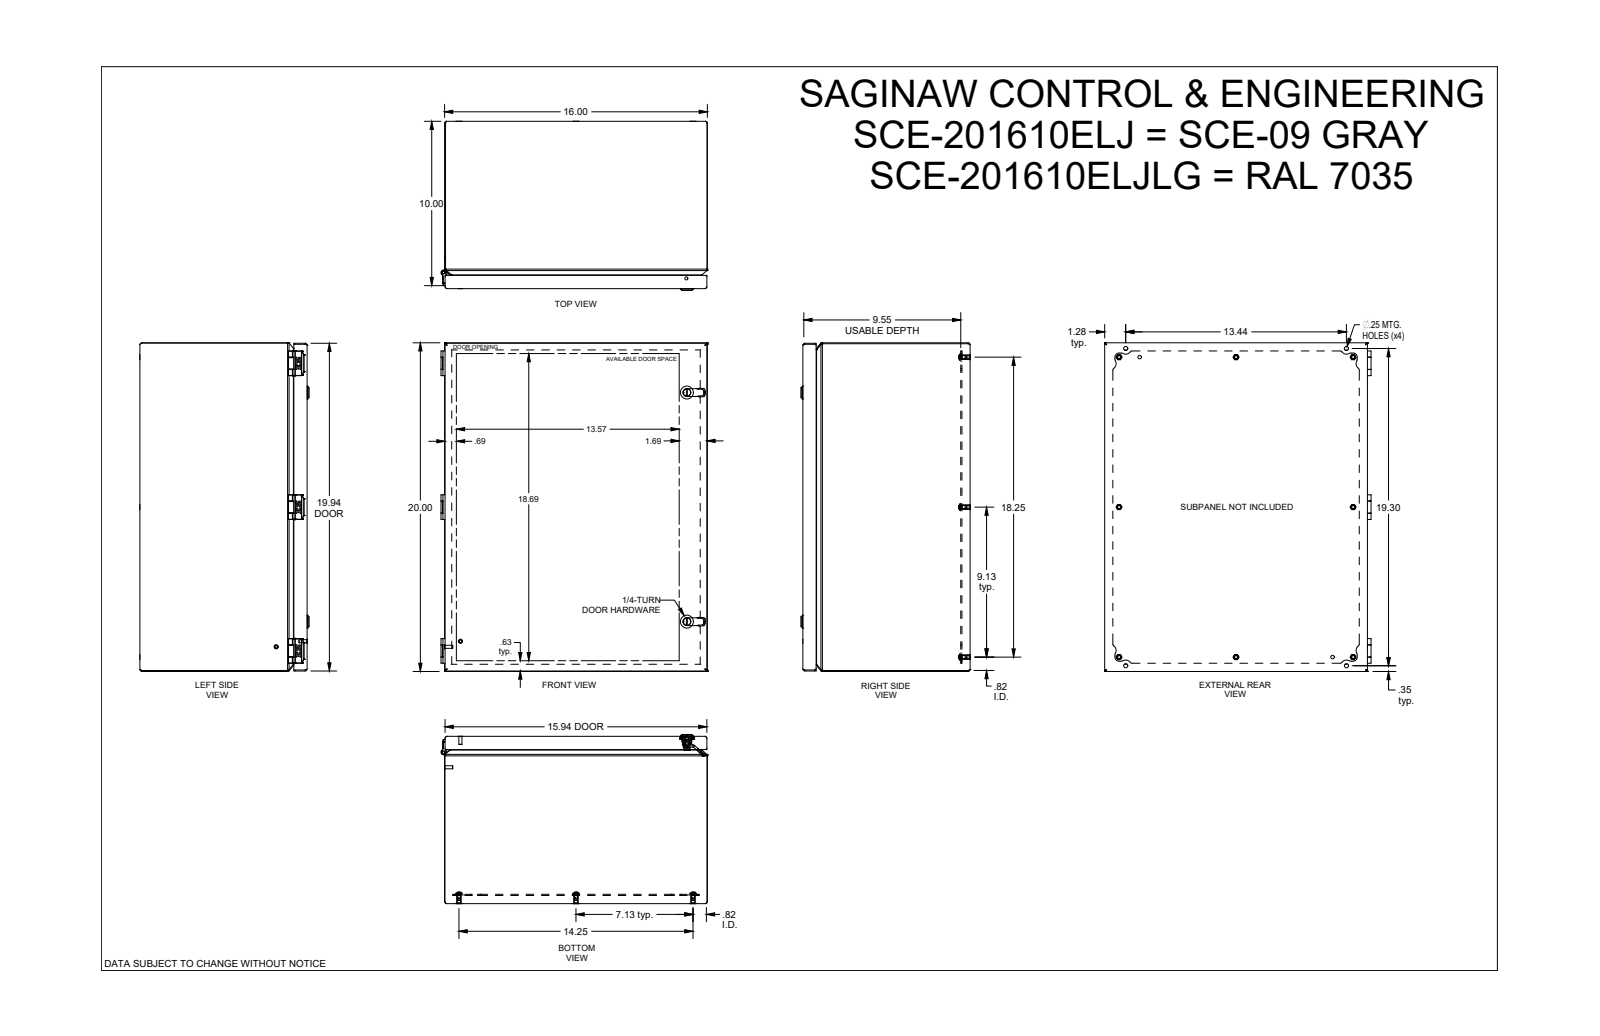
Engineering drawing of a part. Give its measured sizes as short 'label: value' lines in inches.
name: SCE-201610ELJ
written by: SolidWorks 2021 (AUTOMOTIVE_DESIGN)
unit: in
bodies: 36 solids, 2039 faces (647 planar, 582 cylindrical, 810 other)
size: 20 × 16.22 × 10.292
volume: 106.9 in³; area: 3 435 in²
holes: 12× ⌀0.25, 8× ⌀0.284, 3× ⌀0.17, 2× ⌀0.2, 2× ⌀0.218, 2× ⌀0.239, 2× ⌀0.254, 2× ⌀0.269, 2× ⌀0.282, 2× ⌀0.326, 2× ⌀0.475, 2× ⌀0.63
bosses: 9× ⌀0.188, 8× ⌀0.373, 3× ⌀0.479, 3× ⌀0.26, 3× ⌀0.1, 3× ⌀0.02, 2× ⌀0.788, 2× ⌀0.548
rounds: 99× R0.106, 51× R0.005, 48× R0.008, 31× R0.013, 18× R0.01, 18× R0.025, 16× R0.05, 12× R0.25
face distances: 0.059, 0.062, 15.941, 10.185, 10.126, 10.123, 10.064, 19.941, 0.571, 0.512
hole spacings: 6.739, 7.125, 7.125, 0.664, 9.125, 9.659, 14.25, 19.593
